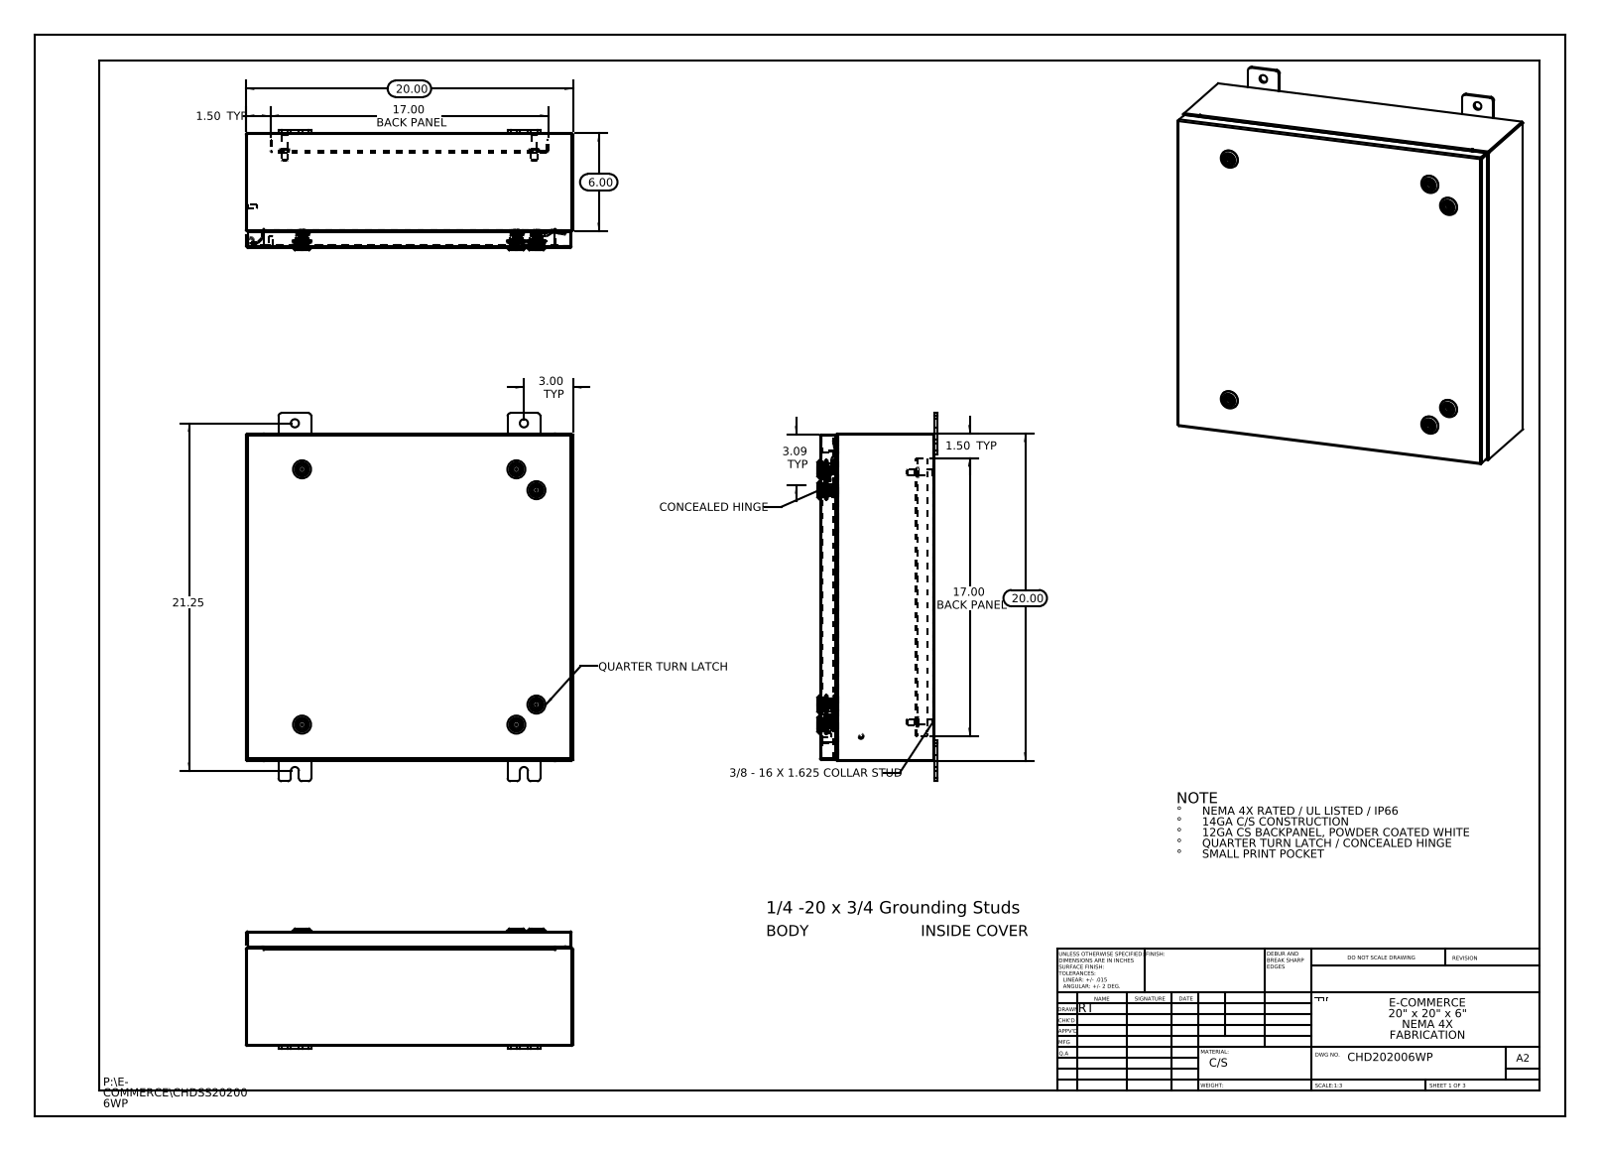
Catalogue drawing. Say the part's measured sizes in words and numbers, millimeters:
The part is named "Screw-221320-IB-Industrilas_Screw-221320-IB-Industrilas; CHDSS202006WP Mounting Studs; CHDSS202006WP Mounting Feet; Quarter-20 CD Stud (+8 more)". Its 3-D file was written by "SolidWorks 2013 (CONFIG_CONTROL_DESIGN)". It is 53 solids with 5376 faces: 1564 planar, 1676 cylindrical and 2136 other. Overall it measures 571.5 by 508 by 186.8 millimeters. Its volume is 2 478 000 cubic millimeters and its surface area 2 427 000 square millimeters. Round holes: 8 of diameter 12.7, 6 of diameter 5, 6 of diameter 10, 6 of diameter 10.2, 6 of diameter 16, 6 of diameter 20, 4 of diameter 3.5. Round bosses or shafts: 8 of diameter 6, 6 of diameter 28, 6 of diameter 19.8, 6 of diameter 15.9, 6 of diameter 15.5, 6 of diameter 13.5, 6 of diameter 10, 6 of diameter 2.9. Partial cylindrical surfaces (rounded edges, fillets, slot ends): 198 of radius 0.2, 198 of radius 3, 72 of radius 0.7, 24 of radius 0.5, 24 of radius 4.8, 24 of radius 5, 20 of radius 0.3, 18 of radius 2.2. The main face-to-face distances are 1.9, 1.9, 506.1, 178.1, 176.1, 176.2, 174.3, 2.6, 25.4, 27.3. The hole center spacings are 332.7, 47.2, 77.9, 355.6, 365.2, 387.4, 387.4, 396.2.
